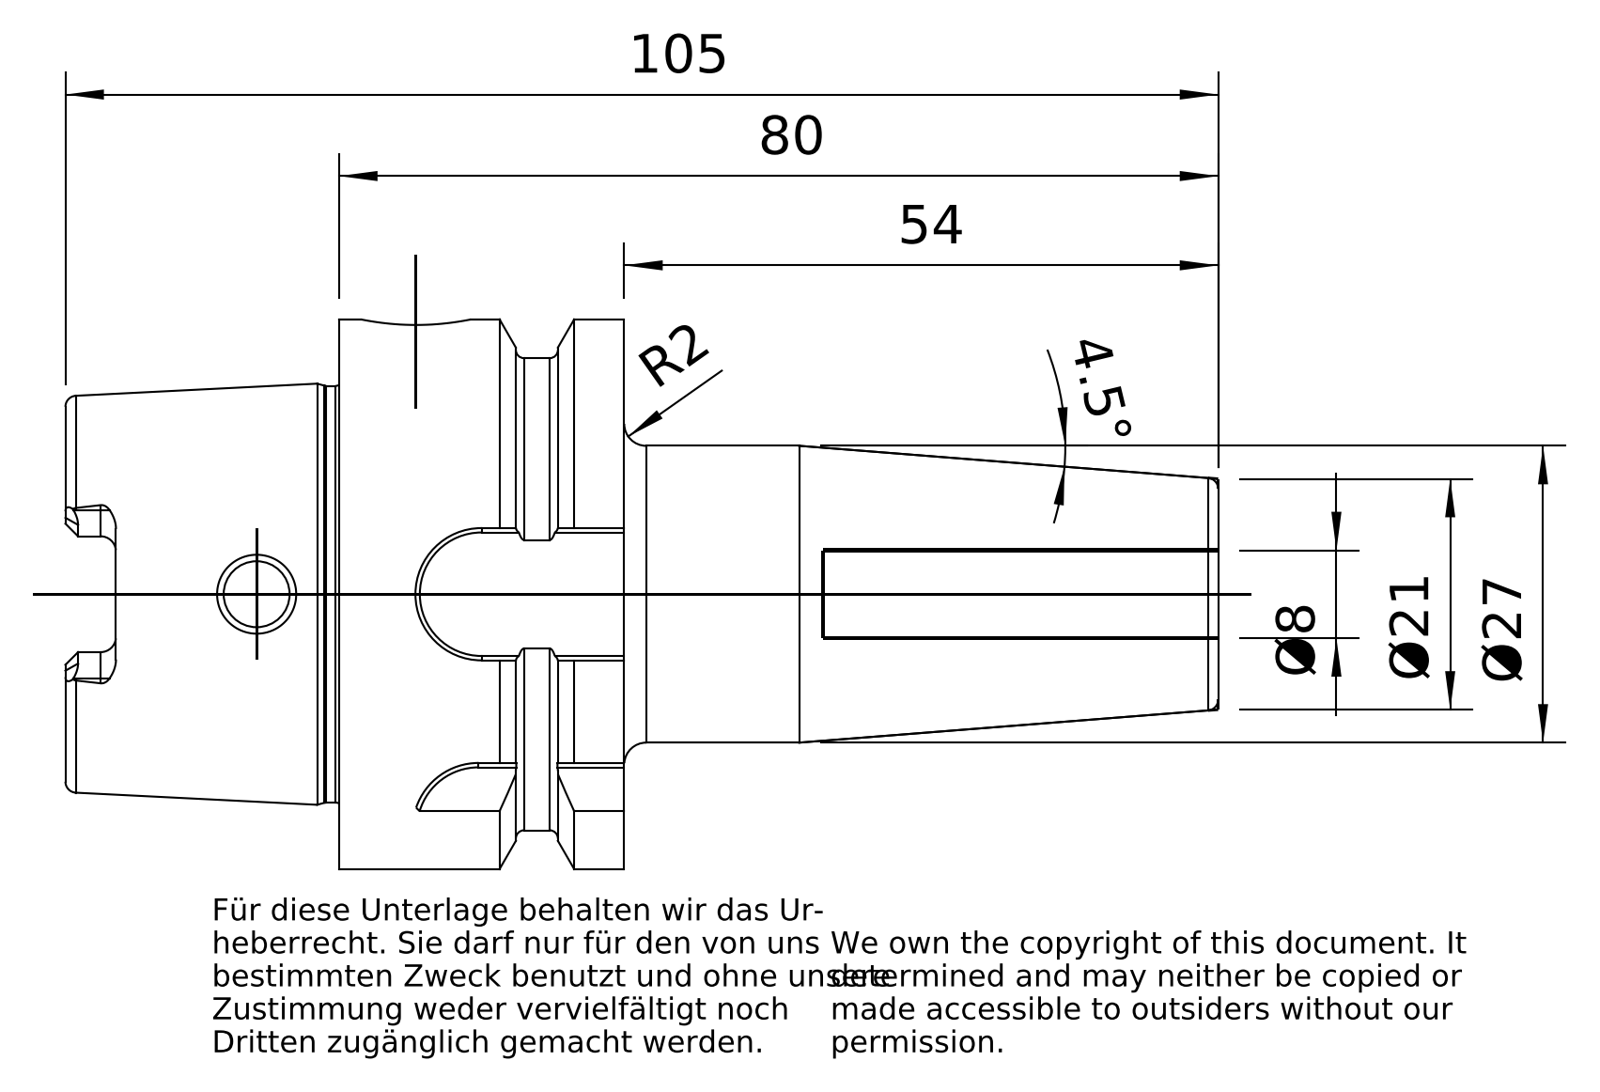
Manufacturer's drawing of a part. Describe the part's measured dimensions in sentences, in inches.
The part is named "A50-140-08". Its 3-D file was written by "PRO/ENGINEER BY PARAMETRIC TECHNOLOGY CORPORATION, 2010430 (CONFIG_CONTROL_DESIGN)". It is 1 solid with 184 faces: 63 planar, 49 cylindrical and 72 other. Overall it measures 4.13 by 1.969 by 1.969 inches. Its volume is 4.49 cubic inches and its surface area 31.2 square inches. Round holes: 1 of diameter 0.236, 1 of diameter 0.315, 1 of diameter 0.394, 1 of diameter 0.551, 1 of diameter 0.63, 1 of diameter 0.643, 1 of diameter 0.65, 1 of diameter 1.025, 1 of diameter 1.263. Round bosses or shafts: 1 of diameter 1.969, 1 of diameter 1.691, 1 of diameter 1.493, 1 of diameter 1.063. Partial cylindrical surfaces (rounded edges, fillets, slot ends): 6 of radius 0.055, 4 of radius 0.094, 3 of radius 0.236, 1 of radius 0.237. The main face-to-face distances are 1.022, 3.15, 2.128, 0.98, 2.002, 4.13, 1.372, 0.392, 0.63, 2.758.
